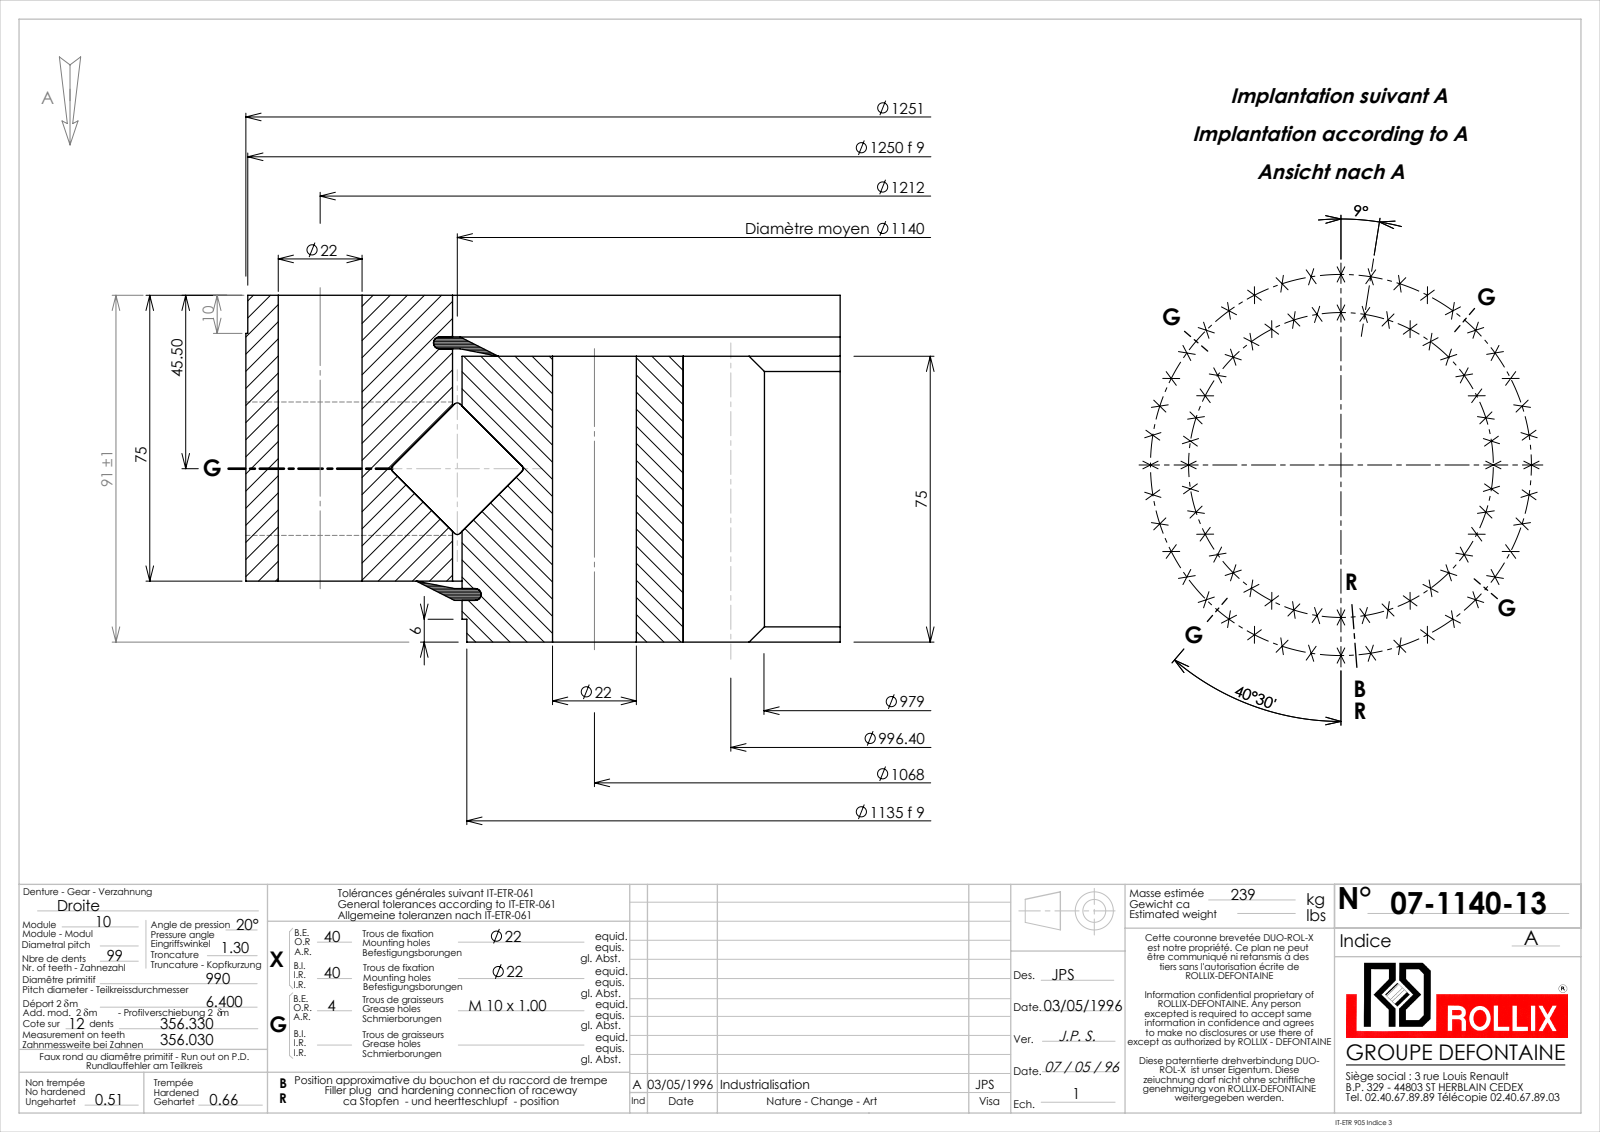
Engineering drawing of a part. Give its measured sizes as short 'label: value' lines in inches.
name: 07-1140-13
written by: SolidWorks 2016 (CONFIG_CONTROL_DESIGN)
unit: in
bodies: 5 solids, 841 faces (214 planar, 387 cylindrical, 240 other)
size: 49.252 × 49.252 × 3.583
volume: 1 750 in³; area: 4 549 in²
holes: 80× ⌀0.866, 4× ⌀0.354, 1× ⌀44.98
bosses: 1× ⌀49.252, 1× ⌀49.213, 1× ⌀44.783, 1× ⌀44.685, 1× ⌀0.984
rounds: 1× R19.272, 1× R20.106
face distances: 2.953, 0.63, 2.323, 3.583, 0.553, 3.03, 0.077, 2.4, 0.431, 3.152
hole spacings: 3.299, 12.993, 37.465, 16.091, 9.816, 24.715, 6.578, 31.973
